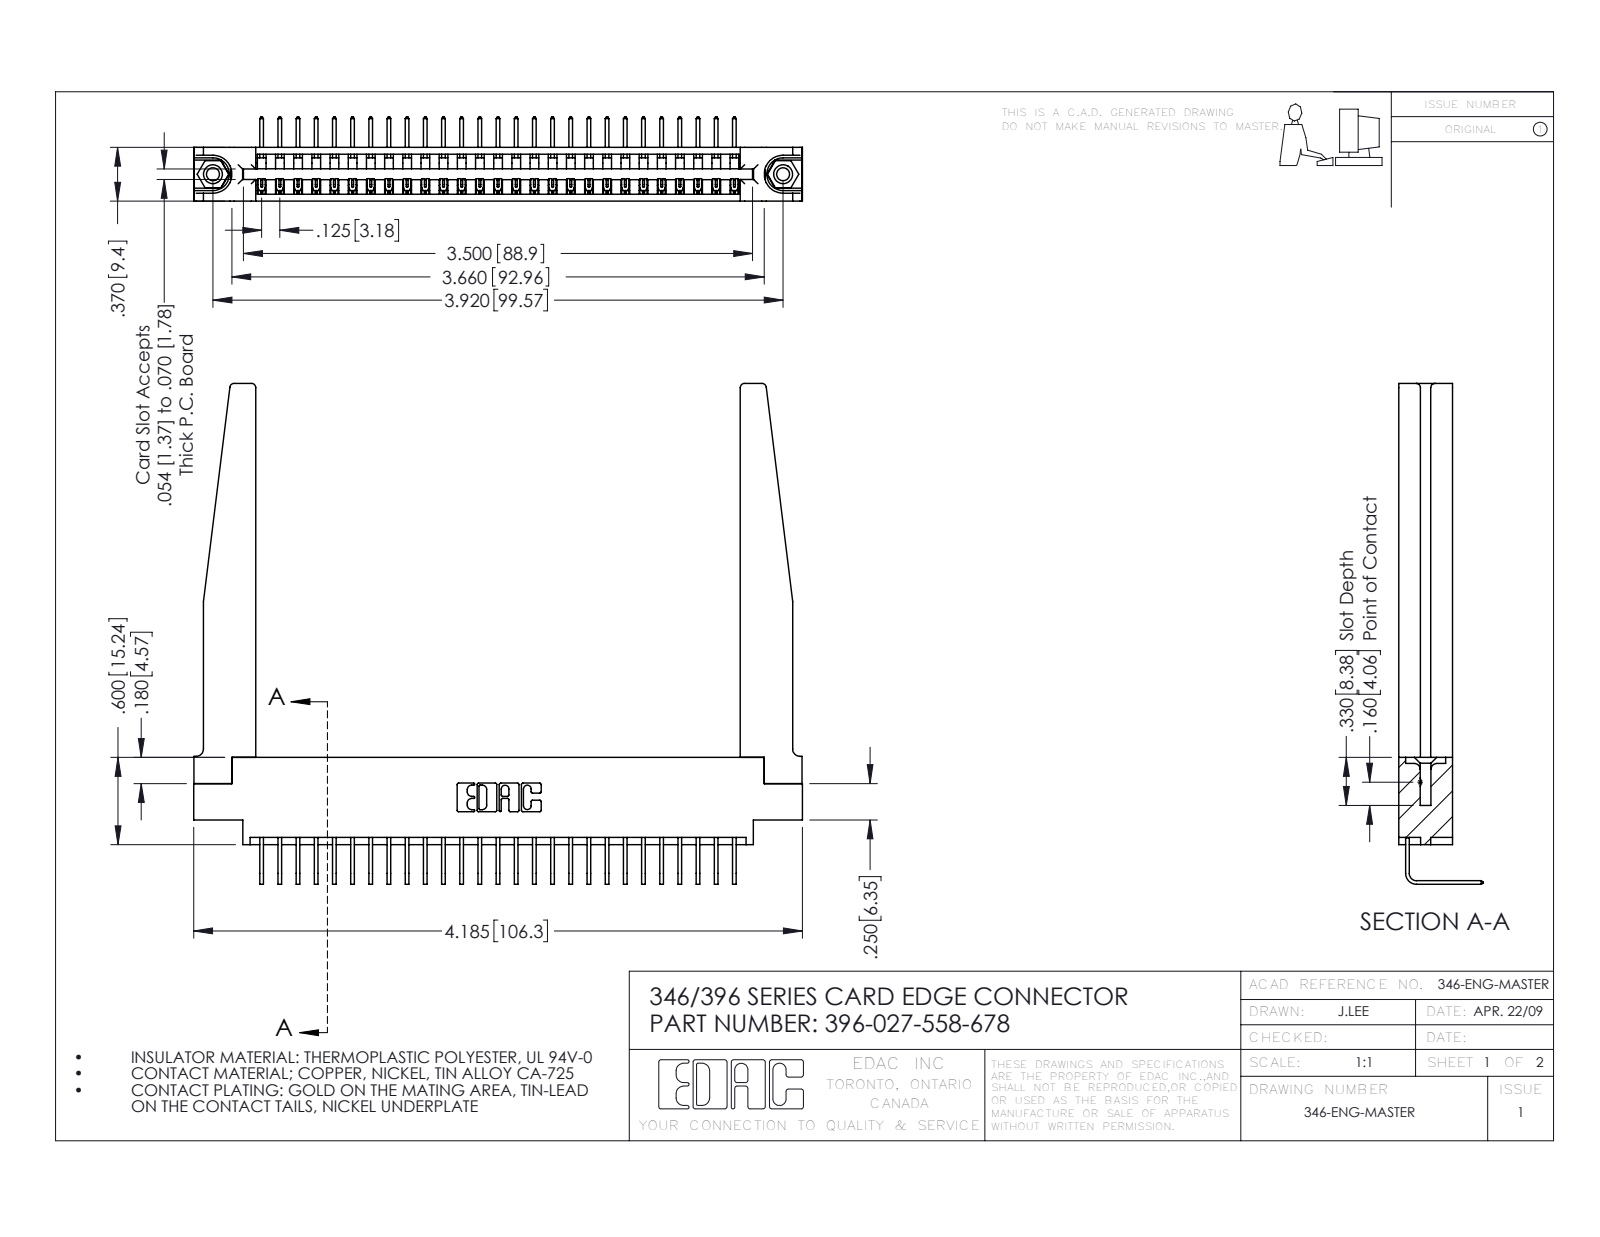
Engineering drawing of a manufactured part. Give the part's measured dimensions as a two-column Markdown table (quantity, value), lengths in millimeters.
| quantity | value |
| --- | --- |
| part name | 345-250-001_345-250-001-102; 346-220-078_345-220-078; 396-027-558-678; 346 Part_0.170 Offset - 0.156 Dia-TH (+1 more) |
| STEP written by | SolidWorks 2016 (CONFIG_CONTROL_DESIGN) |
| units | millimeters |
| bodies | 32 solids, 1980 faces (1356 planar, 572 cylindrical, 52 other) |
| overall size | 106.3 × 87.5 × 14.7 |
| volume | 16 910 mm³ |
| surface area | 19 580 mm² |
| round holes (diameter × count) | 2.3 × 2, 3.2 × 2, 4 × 2, 1.6 × 1 |
| round bosses / shafts (diameter × count) | 3.9 × 2 |
| partial cylindrical surfaces (radius × count) | 0.2 × 54, 0.3 × 22, 0.8 × 8, 0.2 × 6, 0.8 × 6, 0.7 × 3, 1.3 × 3, 0.8 × 2 |
| main face-to-face distances | 9.4, 8.2, 1.2, 1.8, 3.8, 3.8, 6.4, 7.6, 0.6, 5.6 |
| hole center spacings | 6.2, 94.3, 99.6 |
